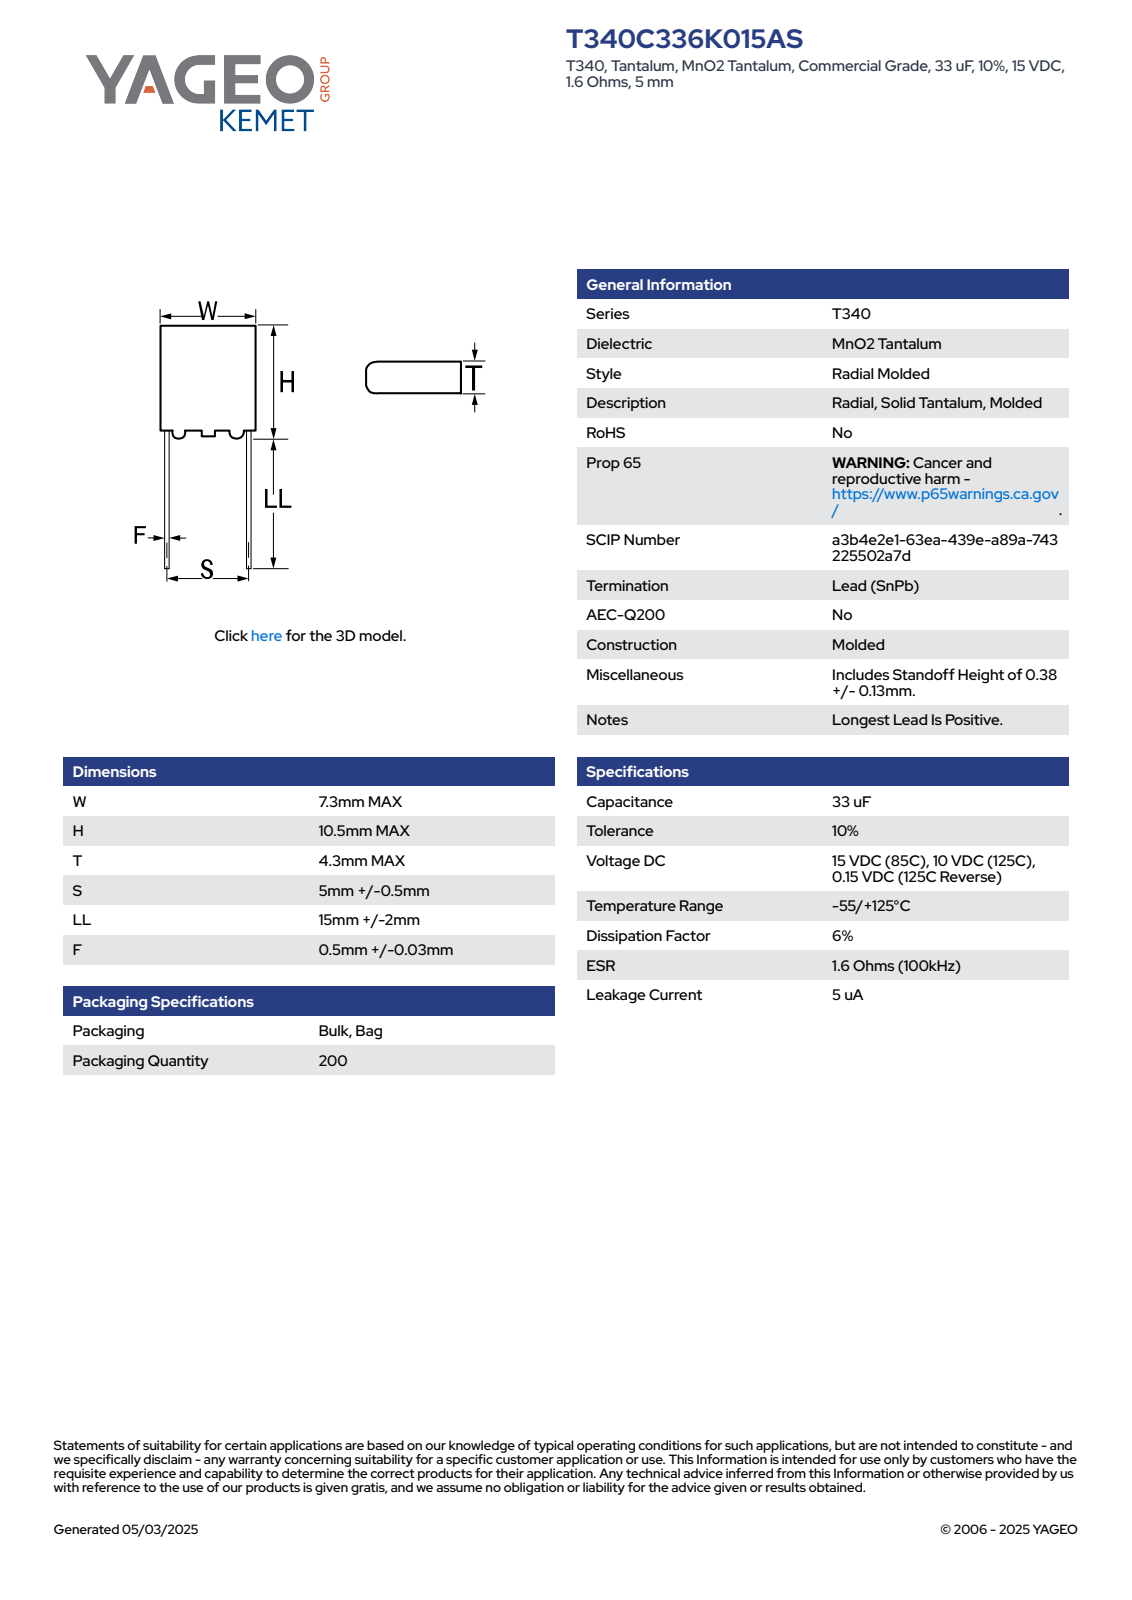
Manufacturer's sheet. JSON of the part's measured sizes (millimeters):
{"part_name": "CTR_T340CDEF_W7.3H10.5T4.3S5LL17F0.53", "step_written_by": "SolidWorks 2014 (AUTOMOTIVE_DESIGN)", "units": "millimeters", "bodies": {"solids": 4, "faces": 79, "planar": 71, "cylindrical": 8, "other": 0}, "overall_size": [27.5, 7.3, 4.3], "volume_mm3": 323, "surface_area_mm2": 363, "round_bosses_or_shafts": [[0.53, 2]], "partial_cylinders_radius": [[0.51, 2], [1, 2]], "face_to_face_distances": [4.3, 7.3, 9.99, 0.51, 10.5, 3.05, 4.25, 1.2, 17, 17.51]}
